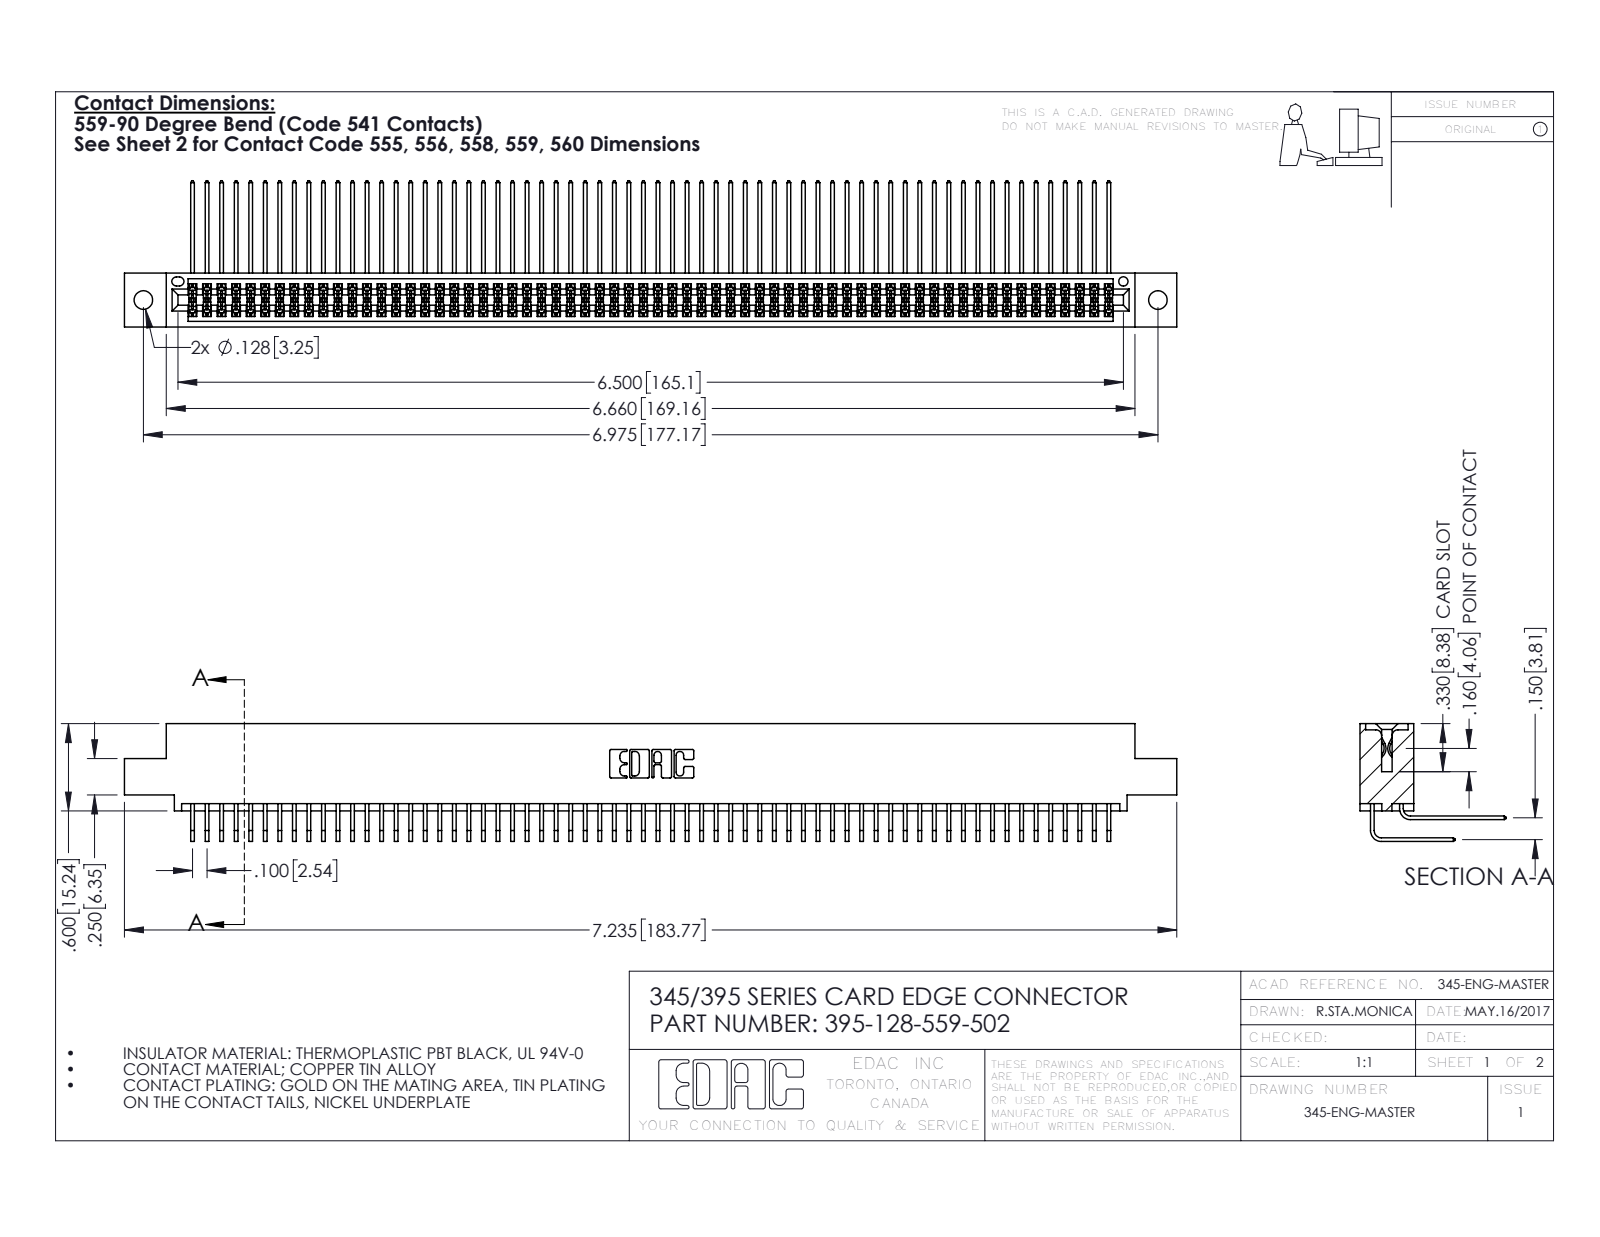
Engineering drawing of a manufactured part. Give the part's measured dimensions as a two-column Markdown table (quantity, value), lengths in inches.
| quantity | value |
| --- | --- |
| part name | 395-128-559-502; 345-292-001_558 559 Tail - 1; 345 Part_0.110 Offset - 0.128 Dia; 345-292-001_559 Tail - 2 |
| STEP written by | SolidWorks 2016 (CONFIG_CONTROL_DESIGN) |
| units | inches |
| bodies | 129 solids, 6786 faces (4564 planar, 2222 cylindrical, 0 other) |
| overall size | 7.235 × 1.005 × 0.809 |
| volume | 1.14 in³ |
| surface area | 48.57 in² |
| round holes (diameter × count) | 0.128 × 2, 0.064 × 1 |
| partial cylindrical surfaces (radius × count) | 0.006 × 193, 0.01 × 22, 0.007 × 6, 0.031 × 6, 0.026 × 3, 0.014 × 2, 0.019 × 2, 0.022 × 2 |
| main face-to-face distances | 0.072, 0.298, 0.2, 0.37, 0.098, 0.272, 0.025, 0.225, 0.175, 0.15 |
| hole center spacings | 0.27, 6.739, 6.975 |
